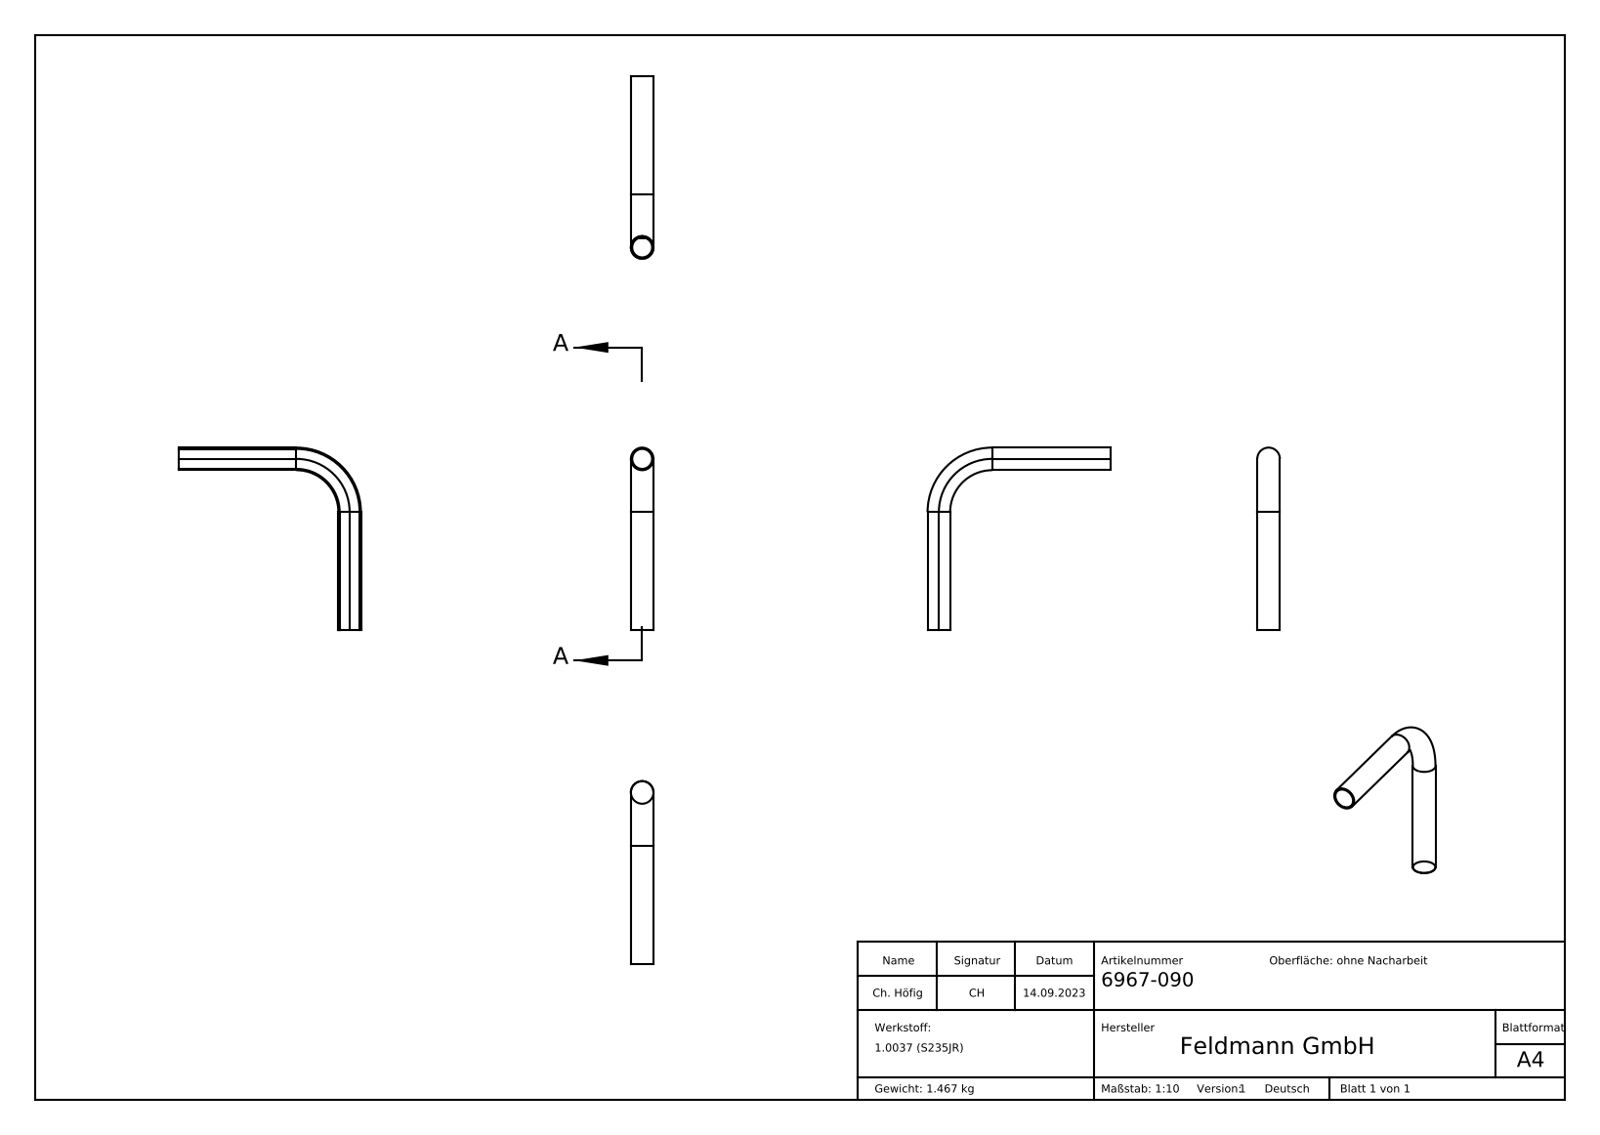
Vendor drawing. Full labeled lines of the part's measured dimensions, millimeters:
Part name (STEP PRODUCT): 6967-090
STEP written by: SolidWorks 2018 (CONFIG_CONTROL_DESIGN)
Units: millimetres
Bodies: 1 solid, 211 faces (103 planar, 4 cylindrical, 104 other)
Overall size (bounding box): 342.66 × 342.66 × 42.4
Volume: 188 024 mm³ · Surface area: 151 050 mm²
Round holes (diameter × count): ⌀37.4 ×2
Round bosses / shafts (diameter × count): ⌀42.4 ×2
Main face-to-face distances: 0.54, 0.49, 0.34, 0.53, 0.58, 0.31, 0.39, 0.48, 0.32
